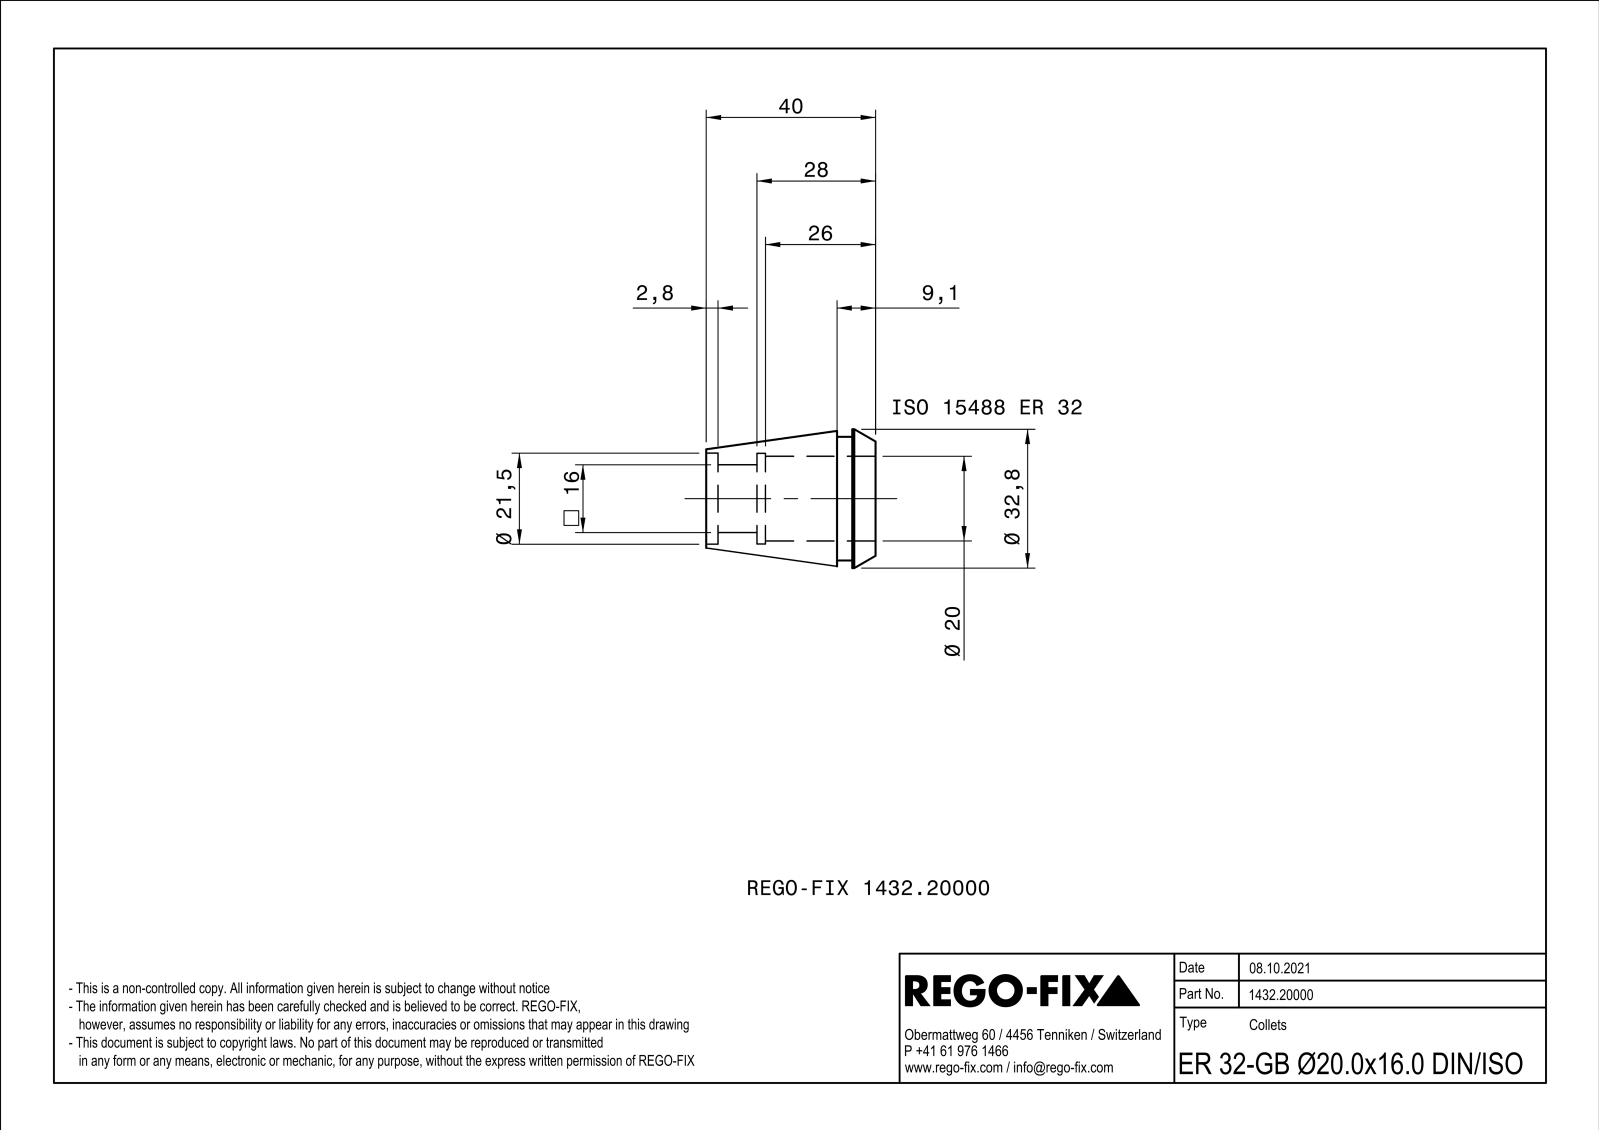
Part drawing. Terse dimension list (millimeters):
name: NOCUT
written by: SIEMENS PLM Software Solid Edge ST10 (AUTOMOTIVE_DESIGN)
unit: mm
bodies: 1 solid, 148 faces (72 planar, 36 cylindrical, 40 other)
size: 40 × 32.79 × 32.79
volume: 11 625 mm³; area: 8 700 mm²
holes: 1× ⌀20, 1× ⌀21.4, 1× ⌀21.5
bosses: 1× ⌀32.8, 1× ⌀29.2
rounds: 1× R9.2, 1× R10.5
face distances: 0.8, 7.9, 8.7, 5.5, 9.1, 3.6, 16.6, 27.8, 22.3, 18.7
